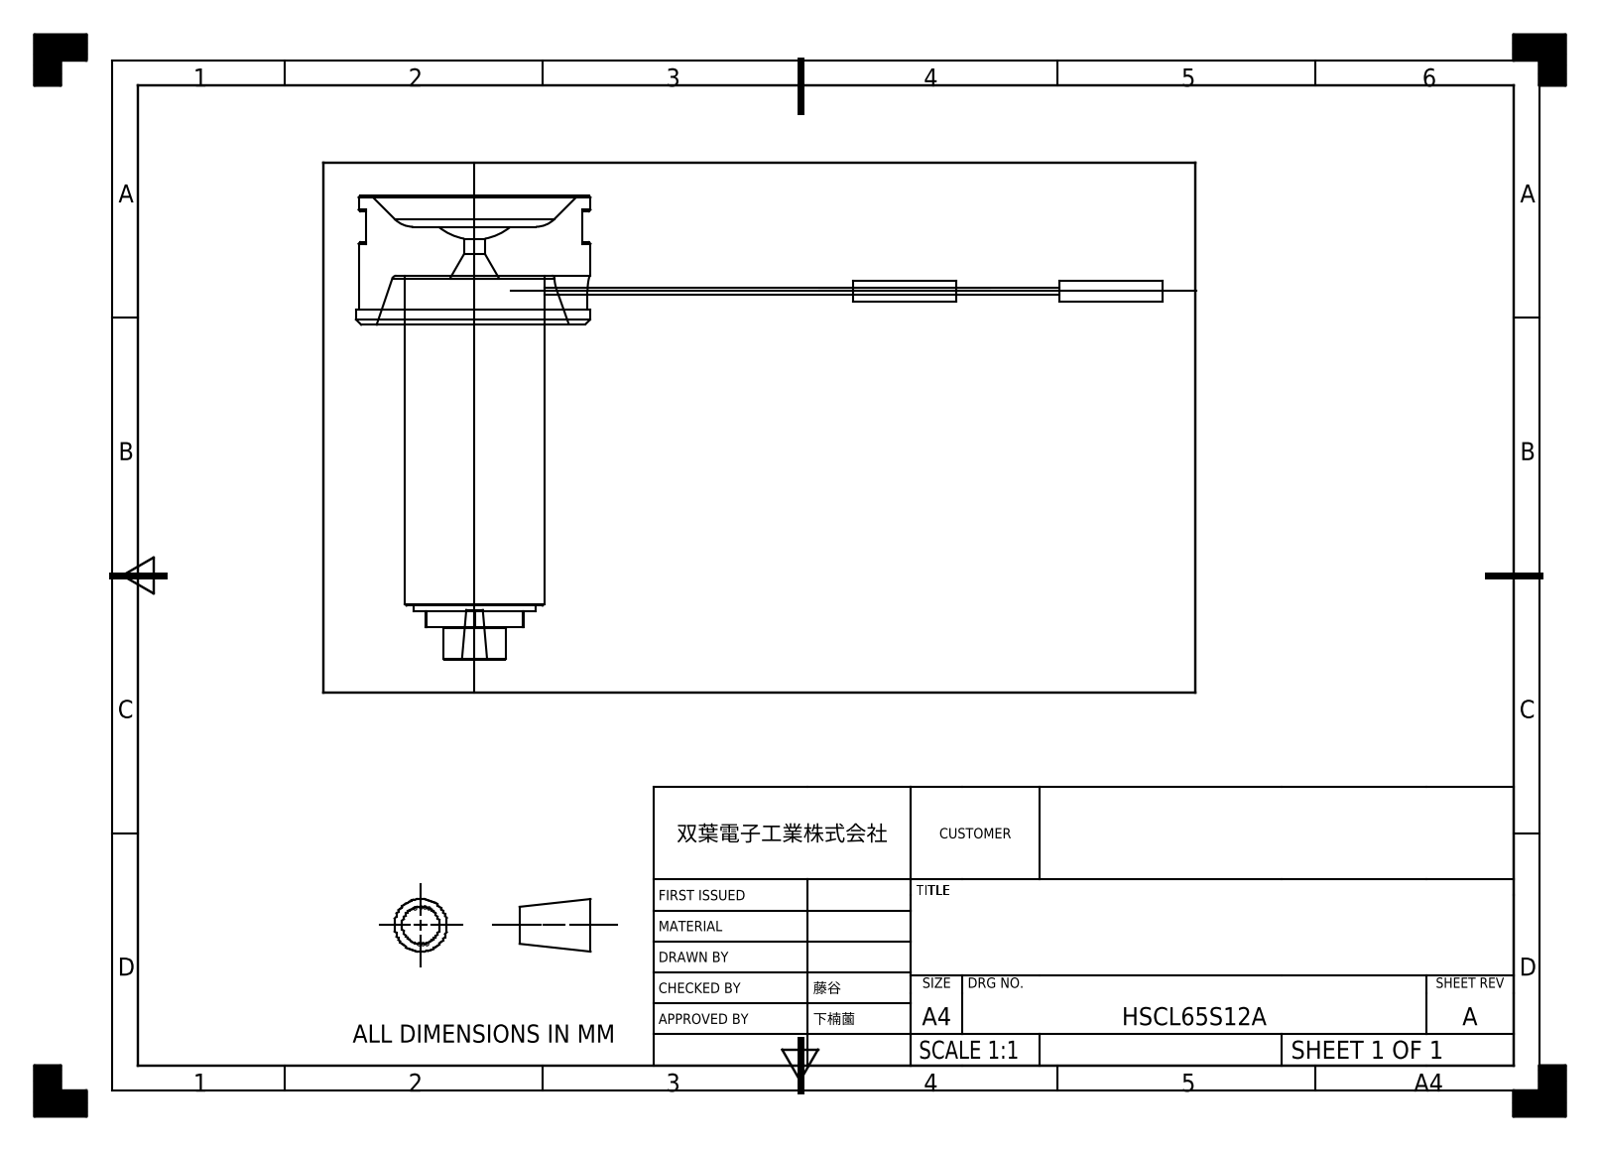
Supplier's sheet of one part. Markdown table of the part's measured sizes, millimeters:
| quantity | value |
| --- | --- |
| part name | HSCL65S12A |
| STEP written by | SIEMENS PLM Software NX 2023 (AUTOMOTIVE_DESIGN) |
| units | millimeters |
| bodies | 5 solids, 67 faces (33 planar, 18 cylindrical, 16 other) |
| overall size | 156.5 × 90 × 46 |
| volume | 63 665 mm³ |
| surface area | 15 138 mm² |
| round holes (diameter × count) | 4 × 1 |
| round bosses / shafts (diameter × count) | 4 × 2, 1.2 × 2, 46 × 1, 45 × 1, 27 × 1, 23.8 × 1, 12 × 1 |
| partial cylindrical surfaces (radius × count) | 3 × 2, 10.9 × 1 |
| main face-to-face distances | 9.5, 19, 6, 25, 74.5, 65, 83.7, 77.7, 58.7, 15.5 |
